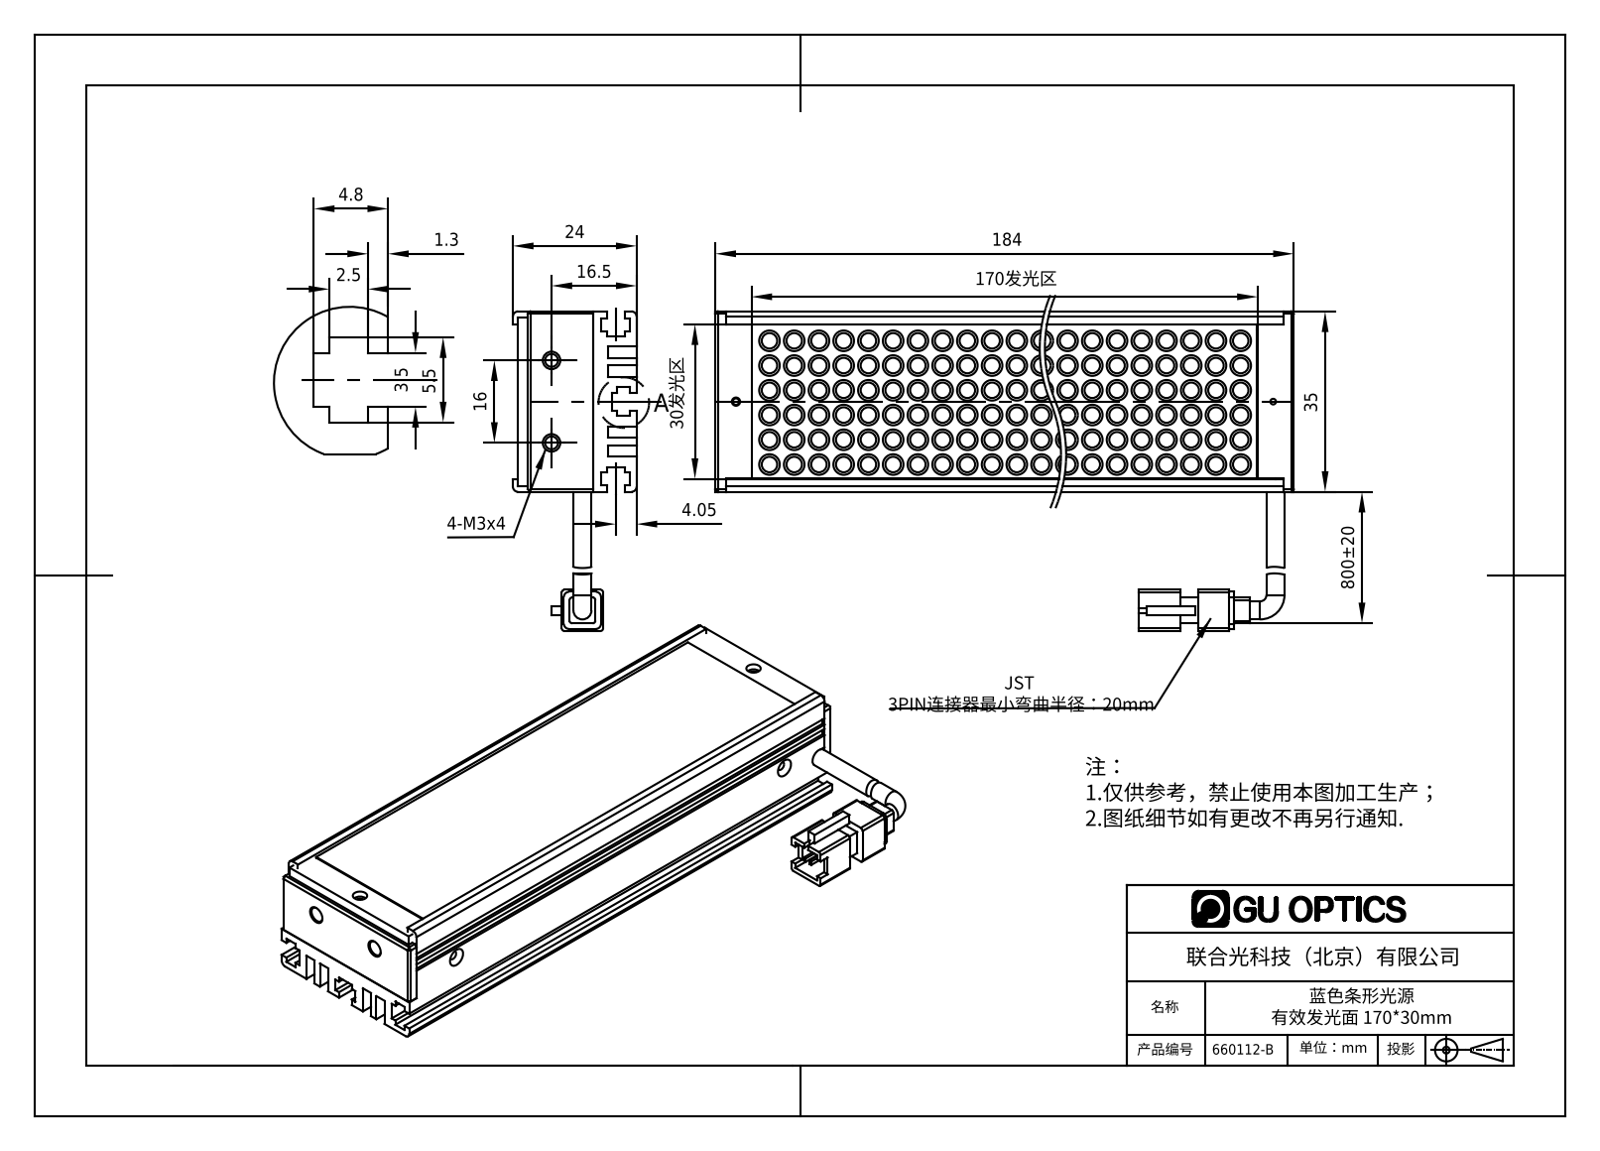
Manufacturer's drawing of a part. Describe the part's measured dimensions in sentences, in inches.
The part is named "660112-B". Its 3-D file was written by "SolidWorks 2016 (AUTOMOTIVE_DESIGN)". It is 8 solids with 1721 faces: 477 planar, 927 cylindrical and 317 other. Overall it measures 7.244 by 2.441 by 0.945 inches. Its volume is 5.049 cubic inches and its surface area 145.6 square inches. Round holes: 5 of diameter 0.063, 3 of diameter 0.067, 2 of diameter 0.059, 2 of diameter 0.098, 2 of diameter 0.11, 2 of diameter 0.118, 1 of diameter 0.043, 1 of diameter 0.049, 1 of diameter 0.079. Round bosses or shafts: 210 of diameter 0.157, 210 of diameter 0.118, 2 of diameter 0.138. Partial cylindrical surfaces (rounded edges, fillets, slot ends): 12 of radius 0.039, 8 of radius 0.02, 1 of radius 0.065. The main face-to-face distances are 0.079, 0.087, 0.339, 0.039, 0.098, 0.496, 0.575, 0.354, 0.157, 0.417. The hole center spacings are 6.929, 0.276, 1.104, 1.123, 2.362, 3.465, 3.471, 5.827.
